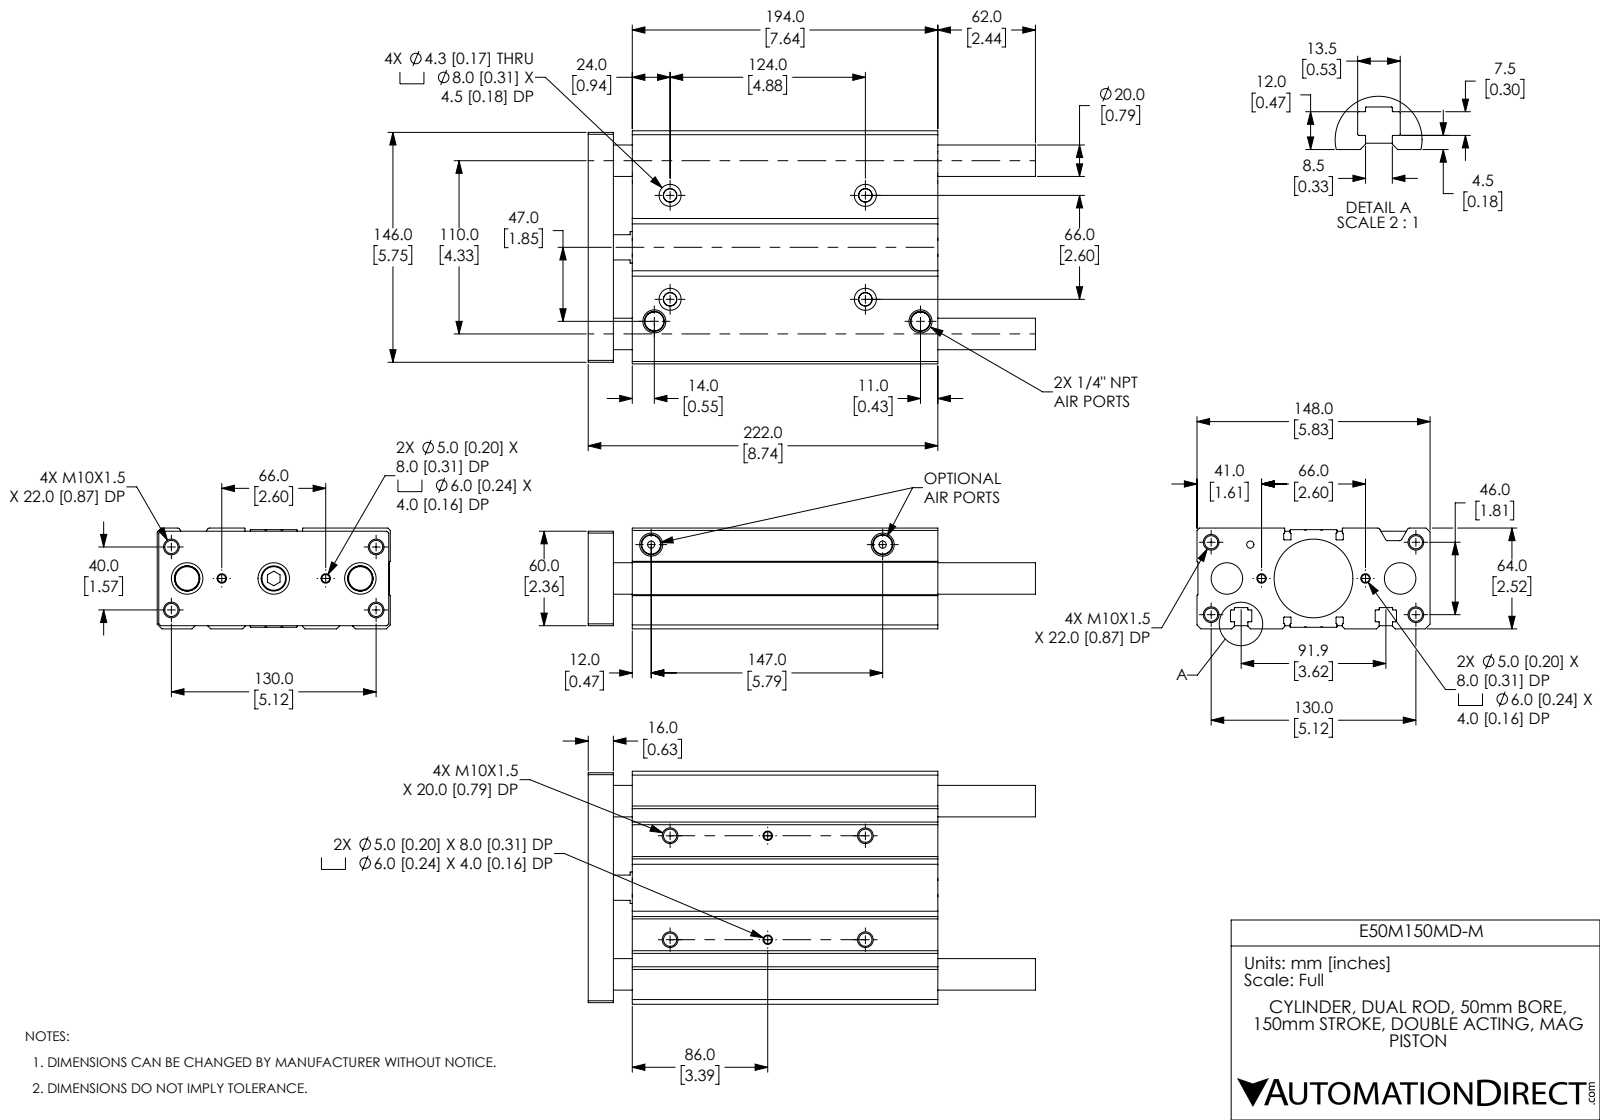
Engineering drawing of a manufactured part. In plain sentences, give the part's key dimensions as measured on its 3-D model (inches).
The part is named "E50M150MD-M_ENDPLATE; E50M150MD-M_BODY; E50M150MD-M". Its 3-D file was written by "SolidWorks 2019 (CONFIG_CONTROL_DESIGN)". It is 5 solids with 423 faces: 139 planar, 190 cylindrical and 94 other. Overall it measures 11.181 by 5.827 by 2.52 inches. Its volume is 98.68 cubic inches and its surface area 432.5 square inches. Round holes: 12 of diameter 0.33, 4 of diameter 0.197, 4 of diameter 0.236, 4 of diameter 0.339, 4 of diameter 0.551, 3 of diameter 0.18, 3 of diameter 0.394, 3 of diameter 0.787, 2 of diameter 0.63, 1 of diameter 0.787, 1 of diameter 1.969, 1 of diameter 1.969. Round bosses or shafts: 1 of diameter 0.63. Partial cylindrical surfaces (rounded edges, fillets, slot ends): 32 of radius 0.008, 28 of radius 0.016, 4 of radius 0.059, 2 of radius 0.012. The main face-to-face distances are 0.039, 2.52, 2.441, 2.48, 0.472, 1.102, 0.63, 5.827, 0.217, 0.024. The hole center spacings are 0.118, 0.88, 0.987, 1.486, 1.552, 1.693, 2.441, 2.598.
